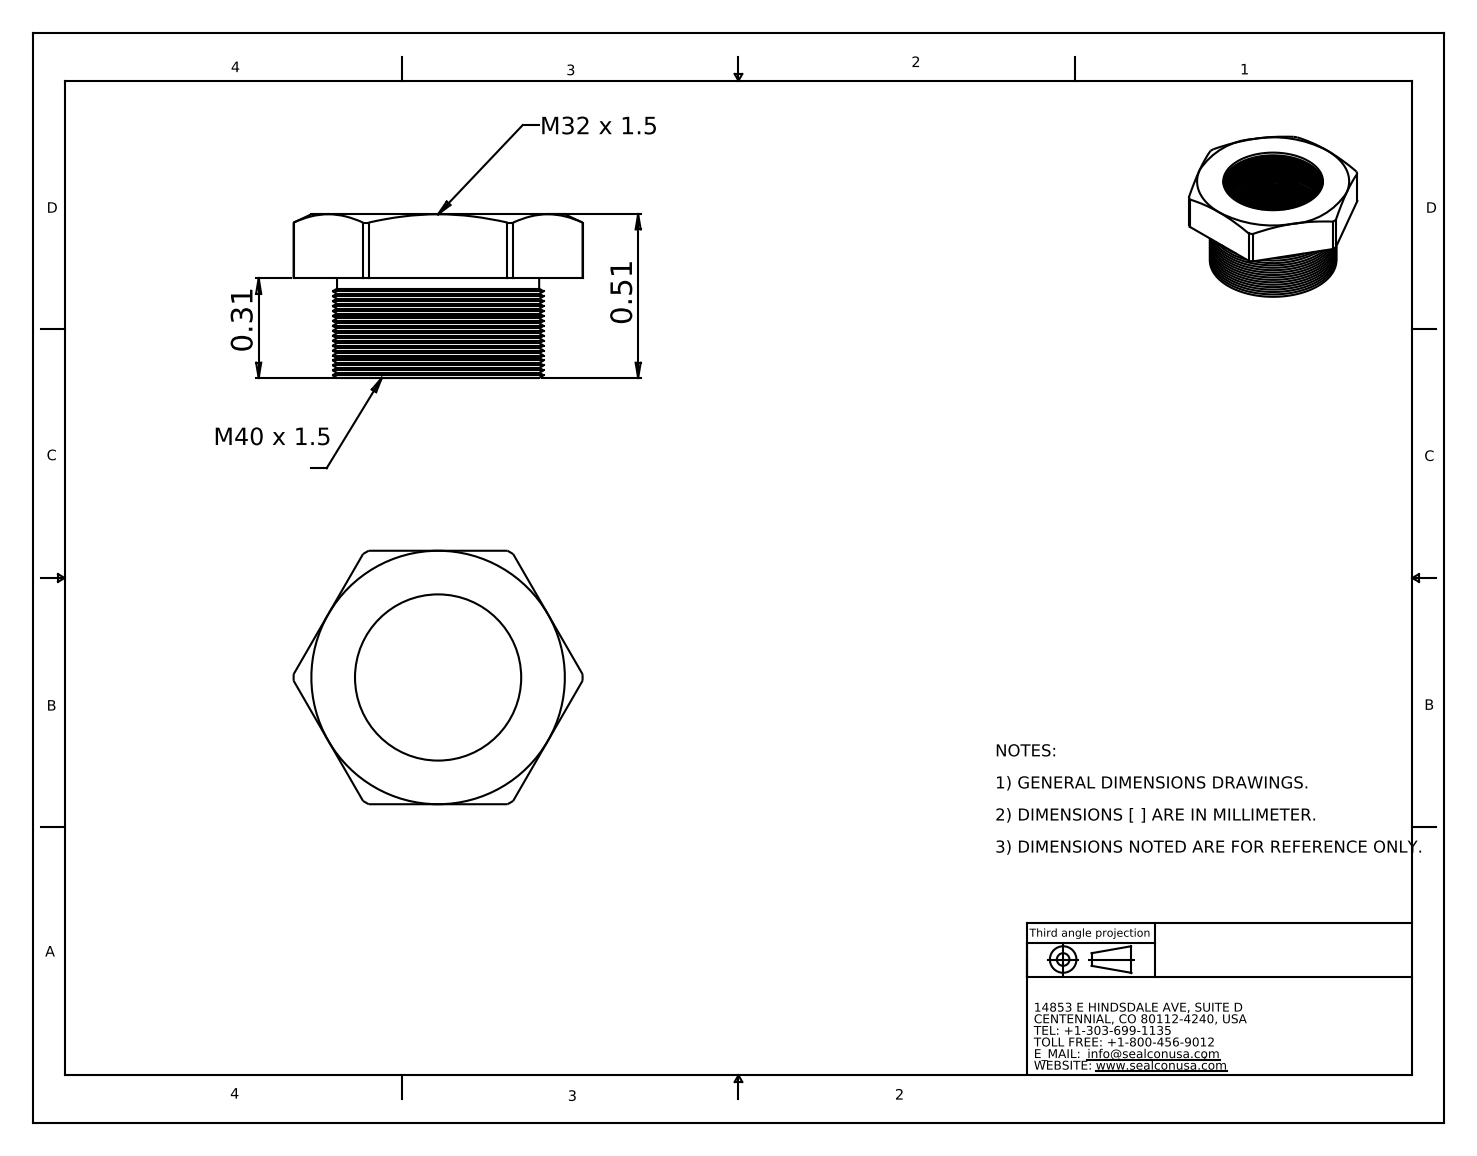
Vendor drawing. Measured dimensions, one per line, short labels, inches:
name: RM-4032-SS
written by: SolidWorks 2008 (CONFIG_CONTROL_DESIGN)
unit: in
bodies: 1 solid, 287 faces (9 planar, 75 cylindrical, 203 other)
size: 0.901 × 0.79 × 0.51
volume: 0.098 in³; area: 4.047 in²
holes: 1× ⌀0.518
bosses: 1× ⌀0.63
rounds: 1× R0.45
face distances: 0.79, 0.2, 0.31, 0.51
